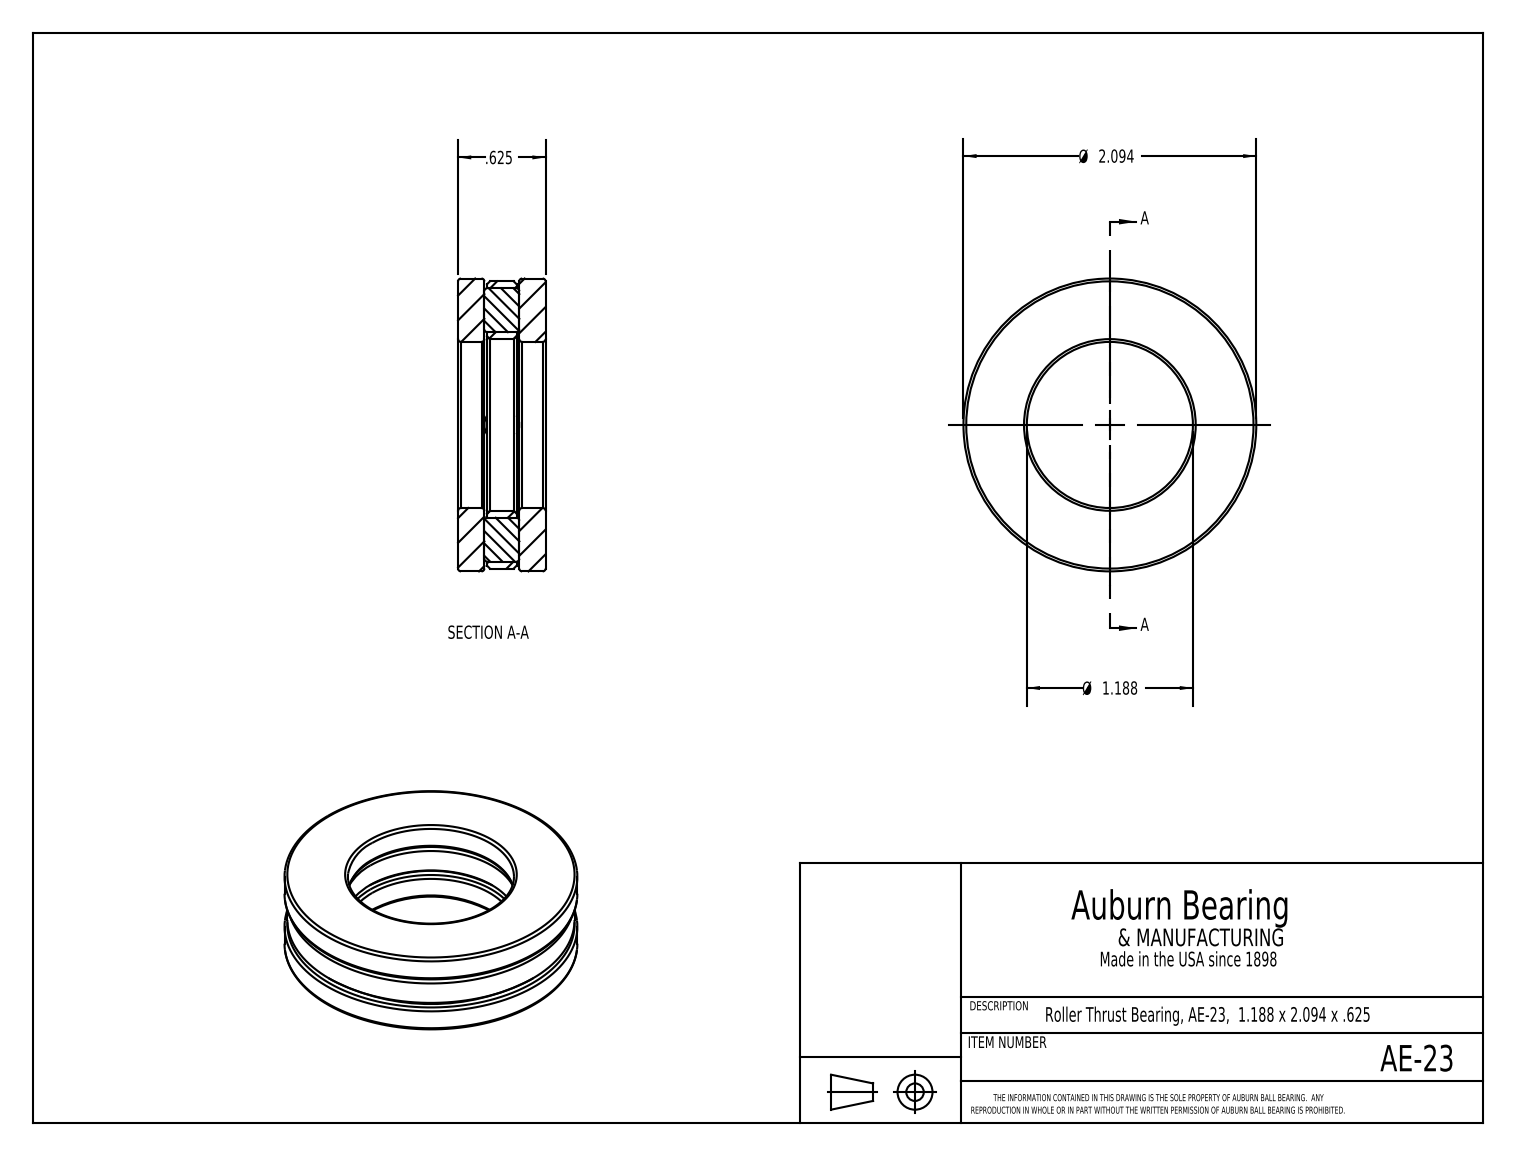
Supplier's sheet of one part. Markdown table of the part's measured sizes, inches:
| quantity | value |
| --- | --- |
| part name | AE-23 |
| STEP written by | SolidWorks 2017 (CONFIG_CONTROL_DESIGN) |
| units | inches |
| bodies | 7 solids, 60 faces (30 planar, 10 cylindrical, 20 other) |
| overall size | 2.094 × 2.094 × 0.625 |
| volume | 1.311 in³ |
| surface area | 20.68 in² |
| round holes (diameter × count) | 1.187 × 1, 1.227 × 1 |
| round bosses / shafts (diameter × count) | 0.25 × 2, 2.094 × 1, 2.054 × 1 |
| main face-to-face distances | 0.207, 0.418, 0.25, 0.187, 0.437, 0.625, 0.438, 0.188, 0.02, 0.23 |
